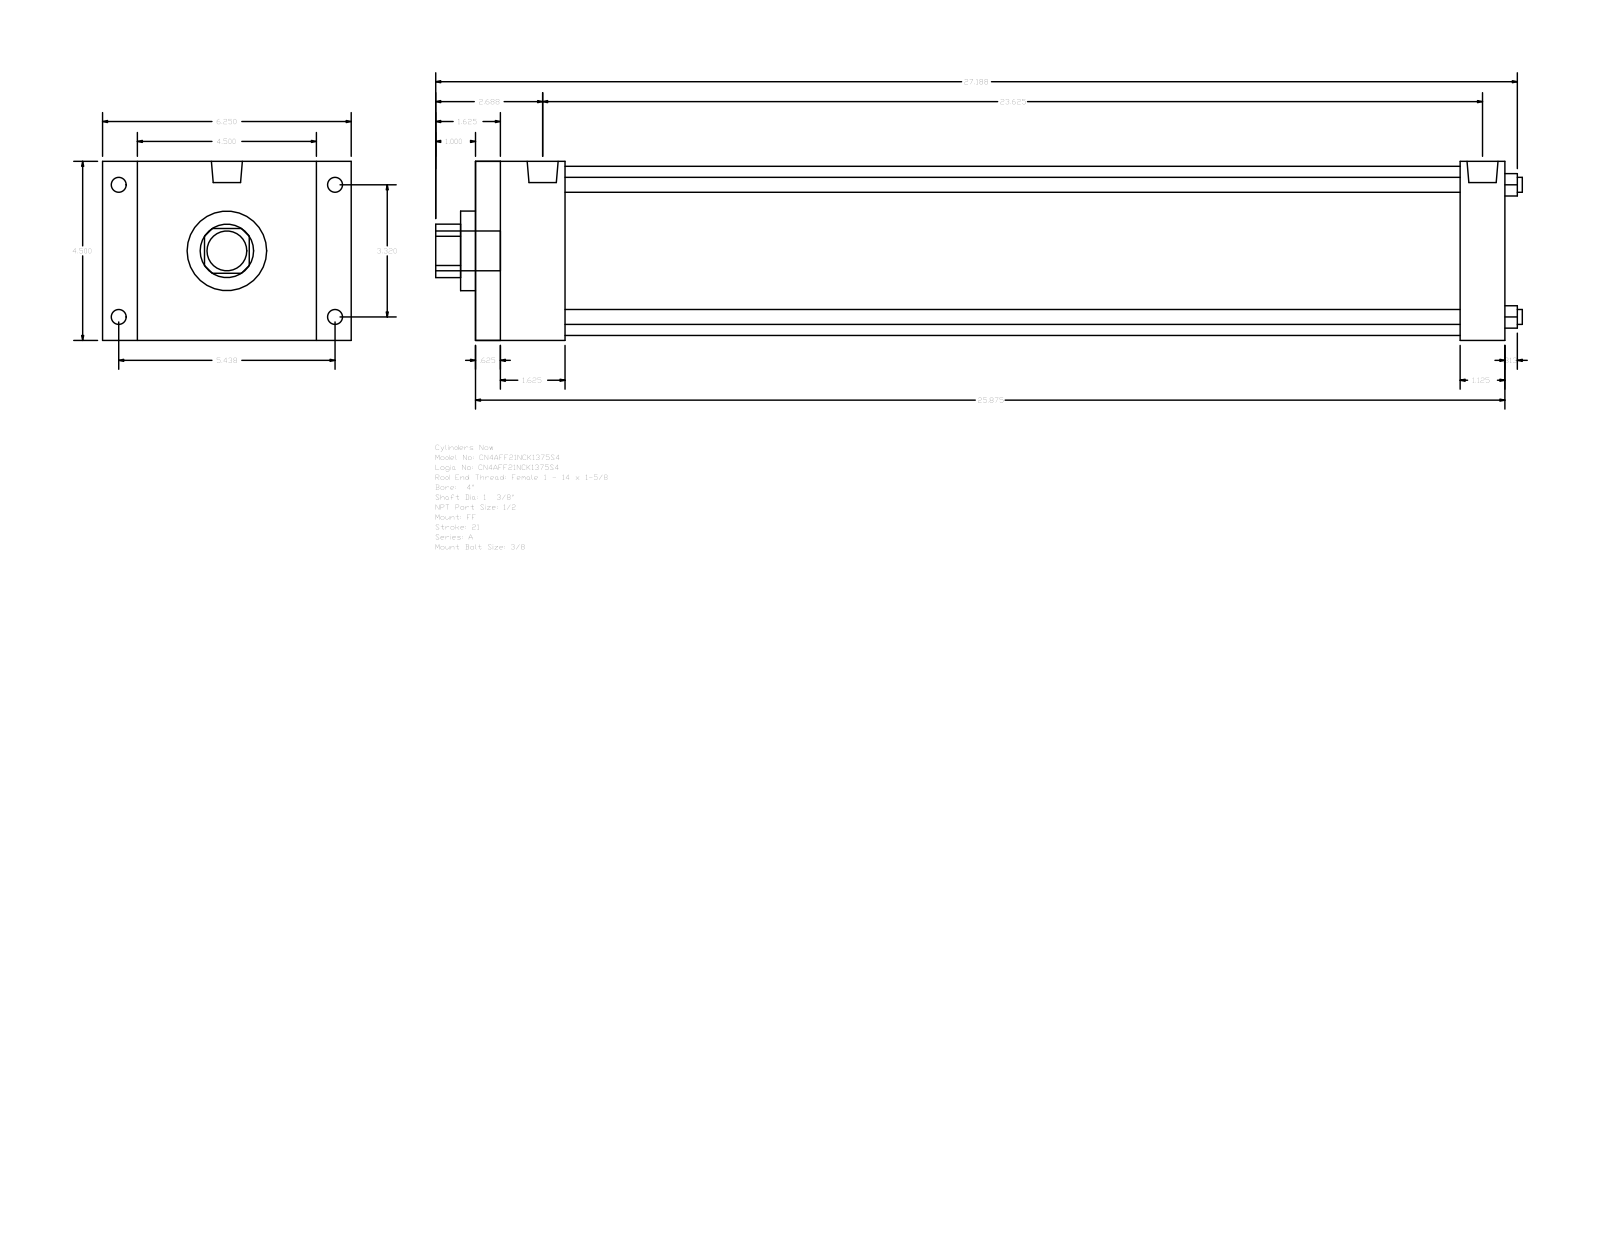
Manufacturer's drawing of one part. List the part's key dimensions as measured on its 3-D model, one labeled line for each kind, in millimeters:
Part name (STEP PRODUCT): A_FF__0400_1.375
STEP written by: GSSL Pune (CONFIG_CONTROL_DESIGN)
Units: millimetres
Bodies: 0 solids, 92 faces (64 planar, 28 cylindrical, 0 other)
Overall size (bounding box): 693.74 × 158.75 × 114.3
Round holes (diameter × count): ⌀9.53 ×4, ⌀34.92 ×1, ⌀50.8 ×1, ⌀107.95 ×1
Round bosses / shafts (diameter × count): ⌀9.53 ×4, ⌀8.73 ×4, ⌀19.77 ×2, ⌀25.4 ×1
Partial cylindrical surfaces — rounded edges, fillets, slot ends (radius × count): R17.06 ×1
Main face-to-face distances: 114.3, 657.22, 641.35, 15.87, 28.57, 22.23, 136.53, 628.65, 612.78, 57.15
Hole centre spacings: 59.62, 84.32, 119.25
